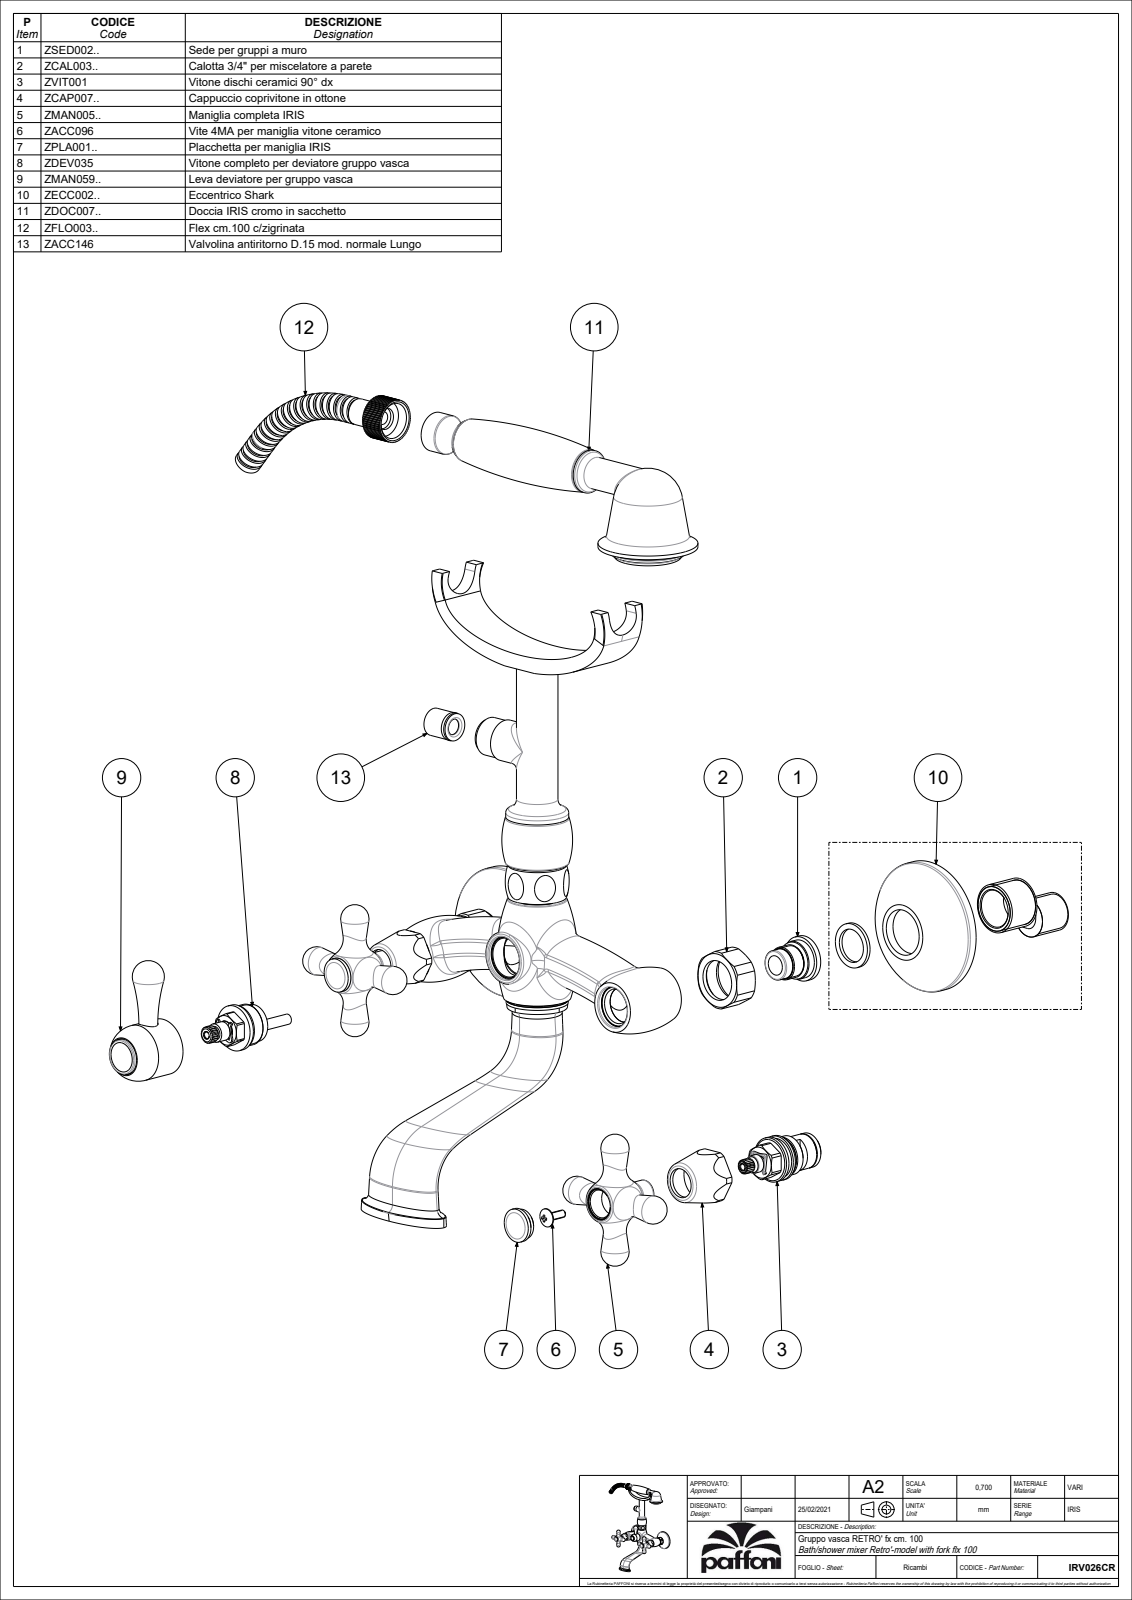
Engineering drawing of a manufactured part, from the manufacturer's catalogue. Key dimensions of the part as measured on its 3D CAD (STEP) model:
Part name (STEP PRODUCT): IRV026CR
STEP written by: CREO PARAMETRIC BY PTC INC, 2020044 (CONFIG_CONTROL_DESIGN)
Units: millimetres
Bodies: 6 solids, 922 faces (252 planar, 154 cylindrical, 516 other)
Overall size (bounding box): 337.51 × 298.8 × 165.62
Volume: 616 989 mm³ · Surface area: 177 703 mm²
Round holes (diameter × count): ⌀21.5 ×3, ⌀23 ×3, ⌀24.1 ×3, ⌀8 ×2, ⌀15.7 ×2, ⌀16.7 ×2, ⌀18.63 ×2, ⌀19 ×2, ⌀26.7 ×2, ⌀14 ×1, ⌀15 ×1, ⌀15.5 ×1
Round bosses / shafts (diameter × count): ⌀18 ×3, ⌀70 ×2, ⌀22 ×2, ⌀20.5 ×2, ⌀13.5 ×2, ⌀53 ×1, ⌀44 ×1, ⌀40 ×1
Partial cylindrical surfaces — rounded edges, fillets, slot ends (radius × count): R14.5 ×2, R15.5 ×2, R5.25 ×1, R10 ×1, R14 ×1
Main face-to-face distances: 44, 35.5, 15.5, 20, 23.25, 3.25, 26.5, 8.5, 24, 31.75
Hole centre spacings: 76.3, 150
